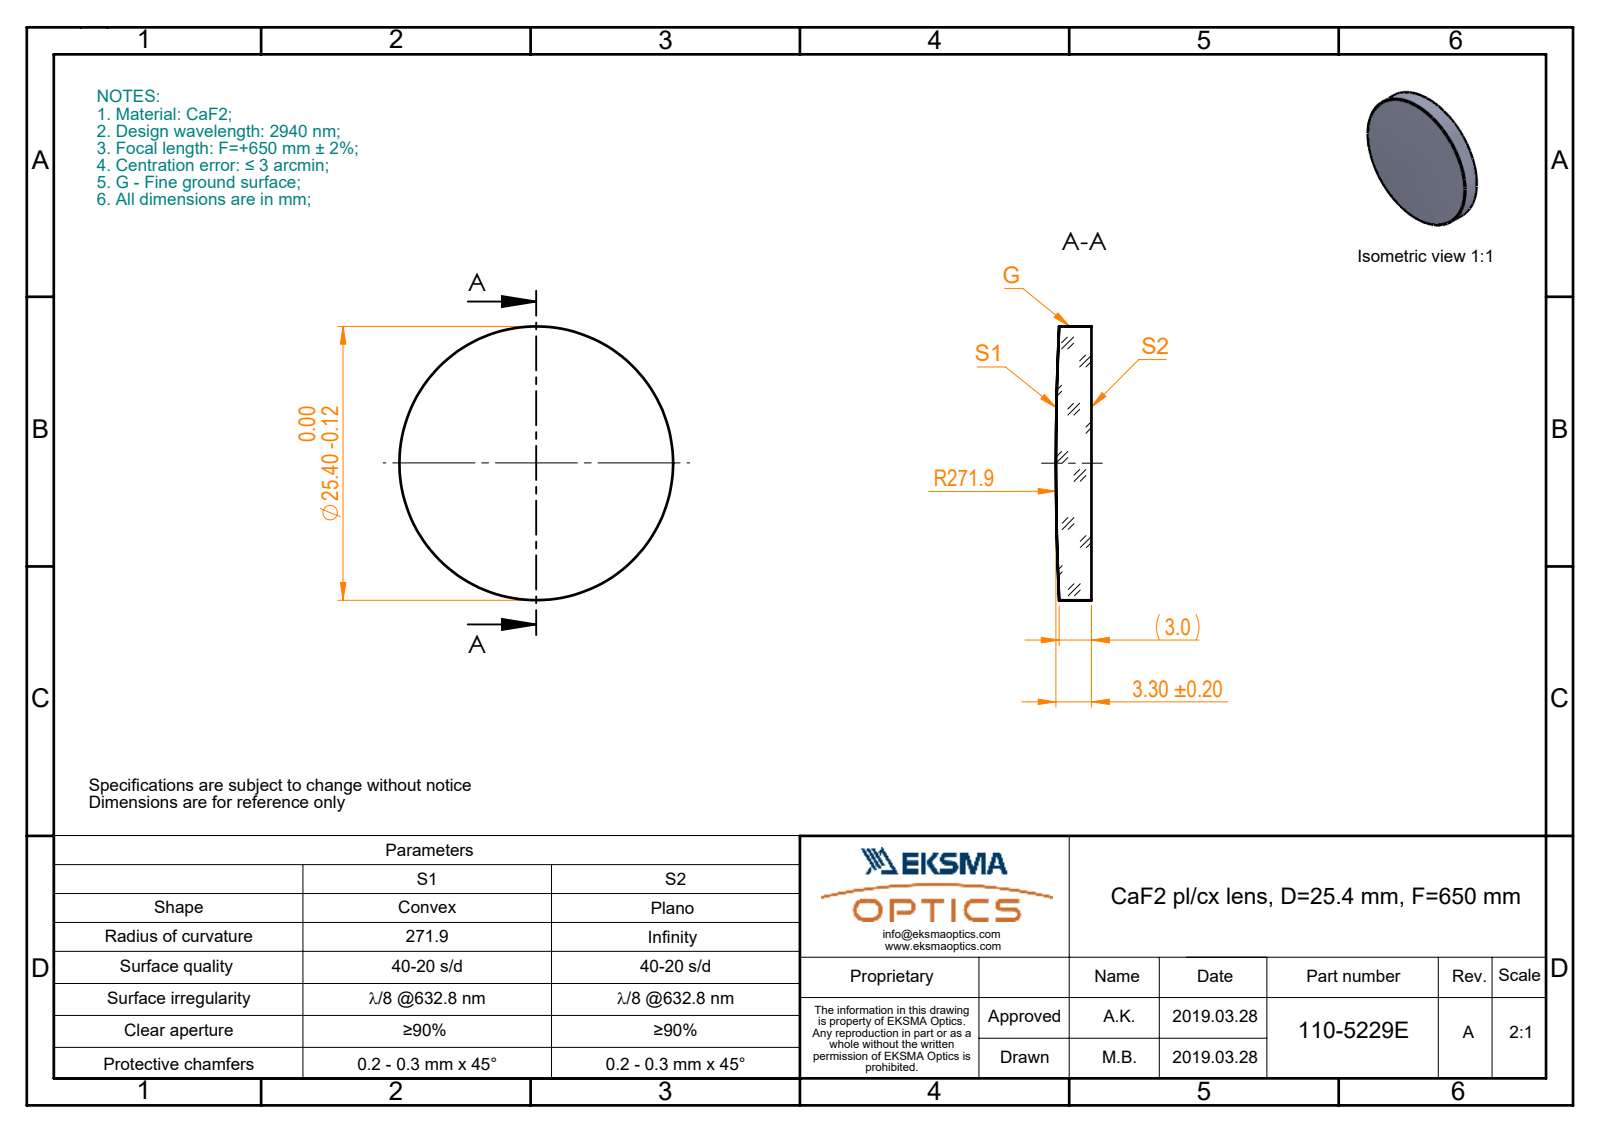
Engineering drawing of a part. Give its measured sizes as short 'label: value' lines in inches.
name: 110-5229E CaF2 pl-cx 25.4 F650
written by: SolidWorks 2017 (CONFIG_CONTROL_DESIGN)
unit: in
bodies: 1 solid, 5 faces (1 planar, 2 cylindrical, 2 other)
size: 1 × 1 × 0.13
volume: 0.097 in³; area: 1.942 in²
bosses: 1× ⌀1
